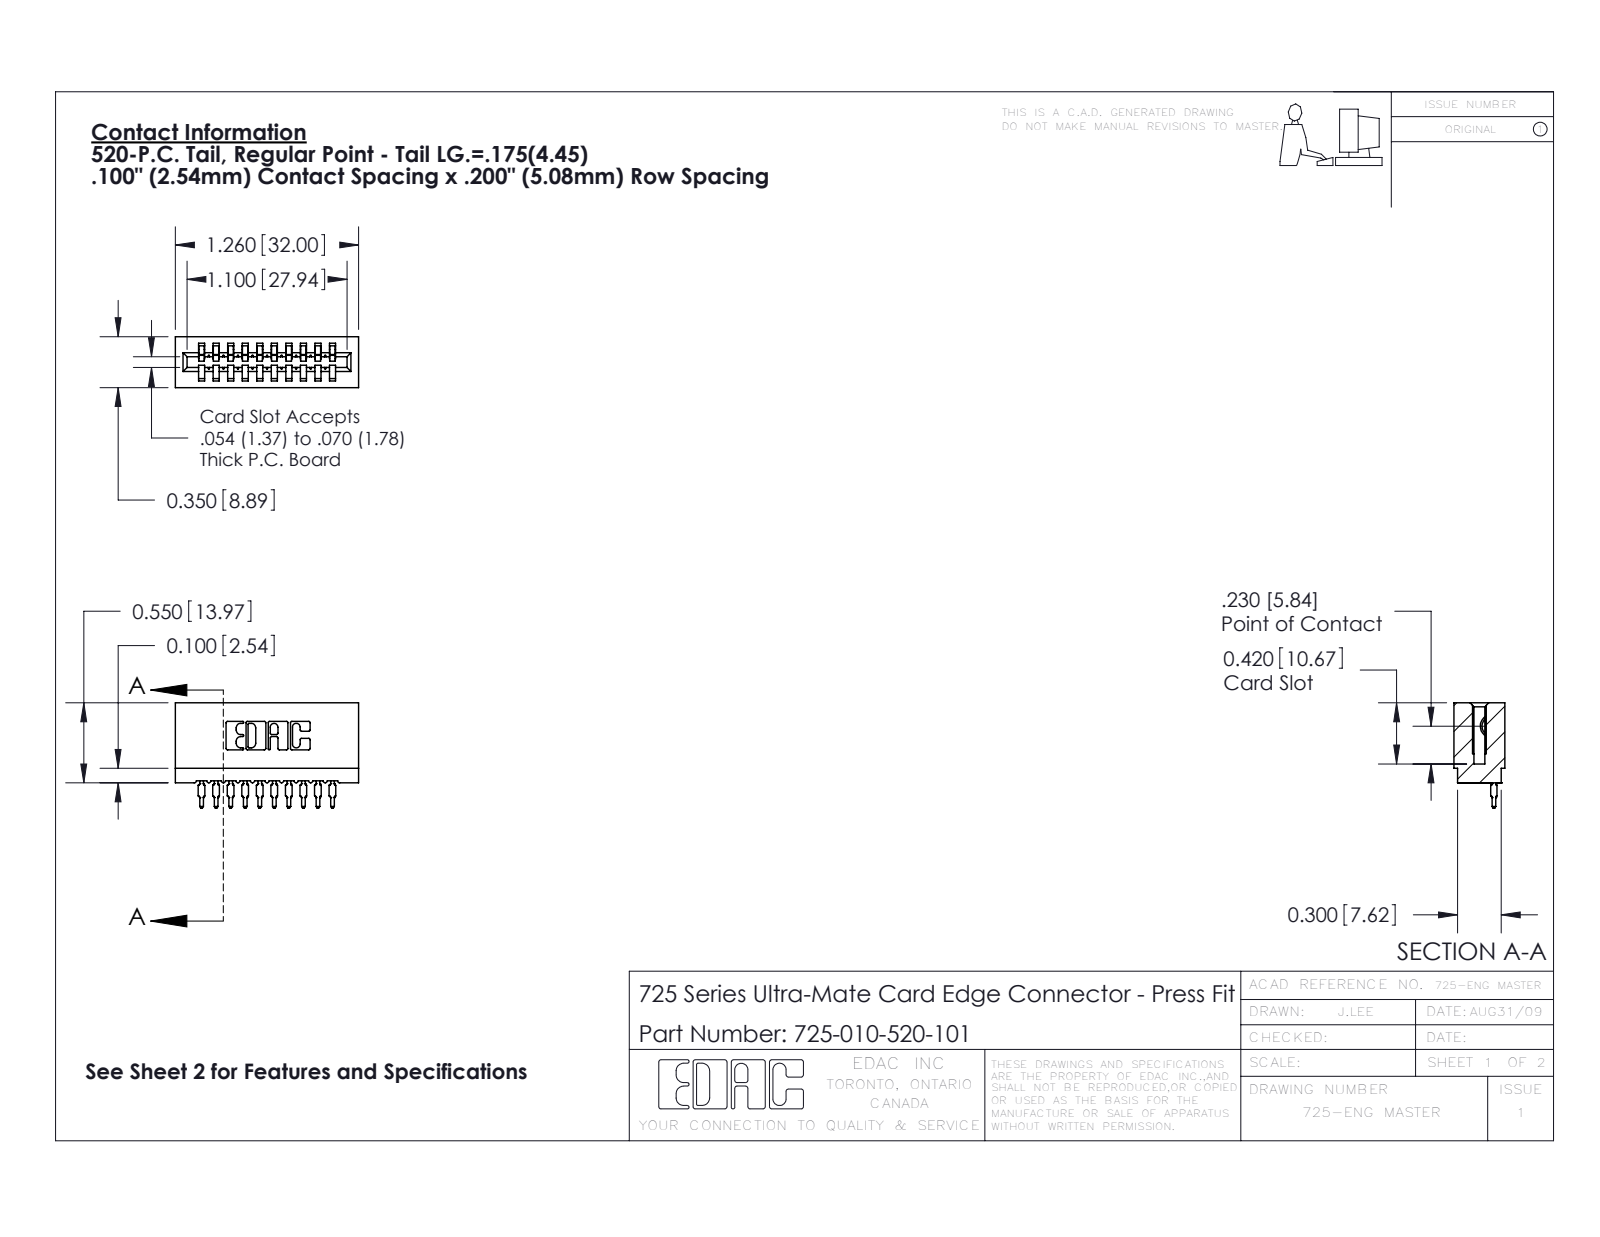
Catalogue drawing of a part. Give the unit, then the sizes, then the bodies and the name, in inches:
Units: inches
Overall size (bounding box): 1.26 × 0.725 × 0.35
Partial cylindrical surfaces — rounded edges, fillets, slot ends (radius × count): R0.01 ×22, R0.015 ×20, R0.021 ×20, R0.007 ×6, R0.031 ×6, R0.005 ×4, R0.011 ×4, R0.026 ×3
Main face-to-face distances: 0.1, 0.2, 0.3, 0.4, 0.042, 0.5, 0.142, 0.058, 0.242, 0.158
Volume: 0.158 in³ · Surface area: 6.734 in²
Bodies: 11 solids, 1215 faces (725 planar, 230 cylindrical, 260 other)
Part name (STEP PRODUCT): 745-292-001_520; 725-010-520-101; 725 Part_Insulator Option - 01
STEP written by: SolidWorks 2016 (CONFIG_CONTROL_DESIGN)
